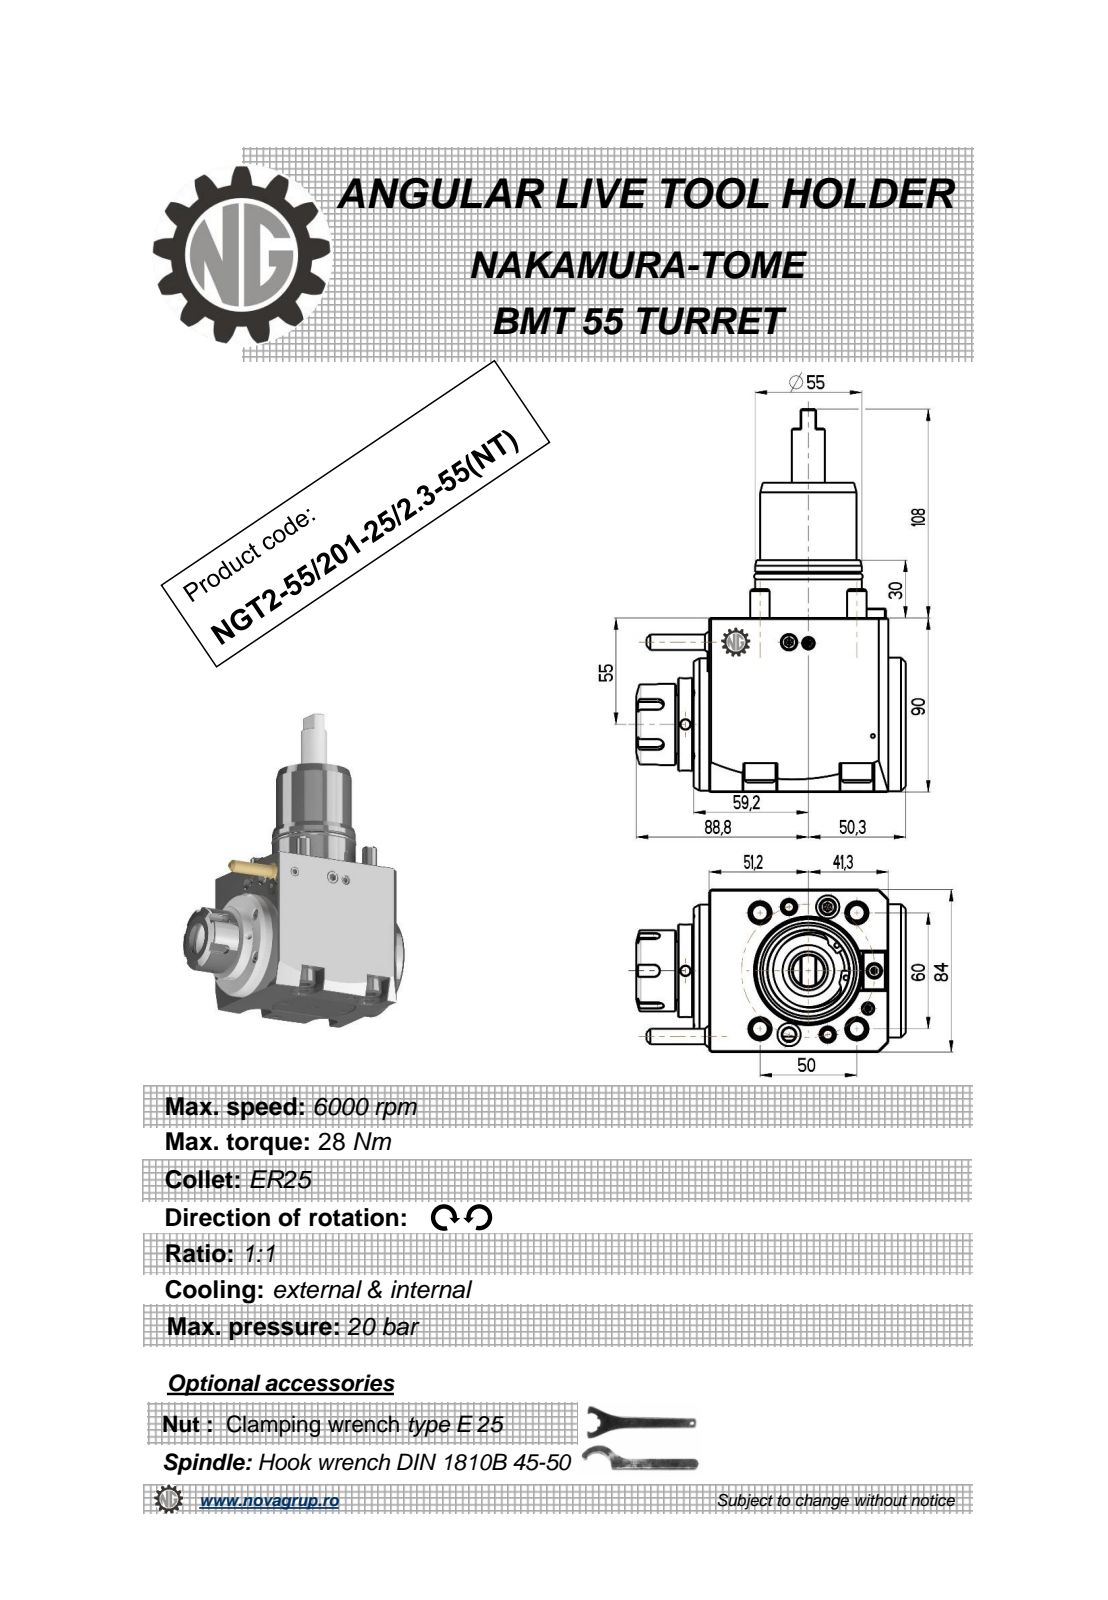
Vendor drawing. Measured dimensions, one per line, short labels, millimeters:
name: NGT2_55_101_32_1_NT
written by: PRO/ENGINEER BY PARAMETRIC TECHNOLOGY CORPORATION, 2010280 (CONFIG_CONTROL_DESIGN)
unit: mm
bodies: 2 solids, 412 faces (186 planar, 107 cylindrical, 119 other)
size: 198 × 139.1 × 84
volume: 946 411 mm³; area: 80 031 mm²
holes: 3× ⌀5, 2× ⌀6.8, 1× ⌀3, 1× ⌀20.3
bosses: 4× ⌀16, 4× ⌀10, 1× ⌀69, 1× ⌀68.5, 1× ⌀55, 1× ⌀50, 1× ⌀49.7, 1× ⌀48
rounds: 20× R0.32, 6× R0.22, 5× R3, 4× R8.5, 2× R0.8, 2× R390
face distances: 84, 90, 8, 101.5, 92.5, 9, 100.5, 109.5, 70, 160
hole spacings: 54.43, 62.82, 68.96, 80.52
